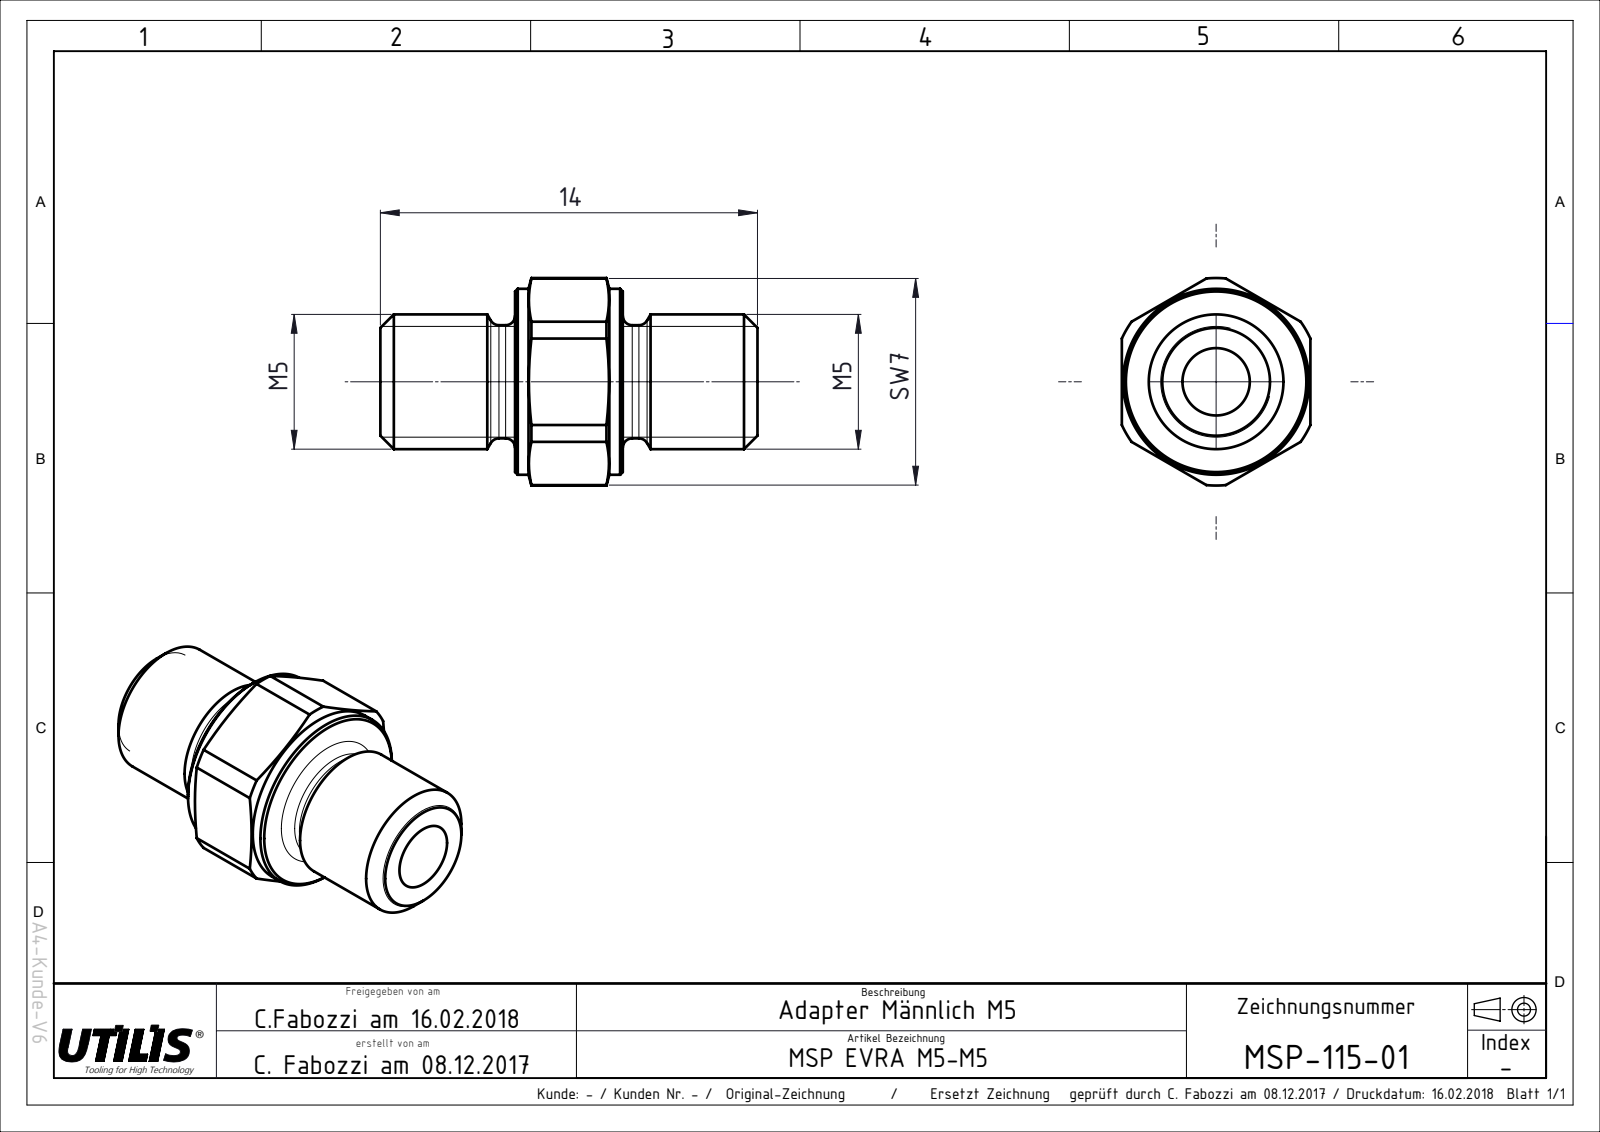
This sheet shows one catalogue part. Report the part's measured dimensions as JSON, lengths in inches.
{"part_name": "MSP-115-01", "step_written_by": "SolidWorks 2017 (AUTOMOTIVE_DESIGN)", "units": "inches", "bodies": {"solids": 1, "faces": 38, "planar": 10, "cylindrical": 16, "other": 12}, "overall_size": [0.551, 0.303, 0.276], "volume_in3": 0.018, "surface_area_in2": 0.649, "round_holes": [[0.098, 1]], "round_bosses_or_shafts": [[0.272, 1], [0.197, 1]], "partial_cylinders_radius": [[0.152, 1]], "face_to_face_distances": [0.276, 0.157, 0.197, 0.354, 0.551]}
